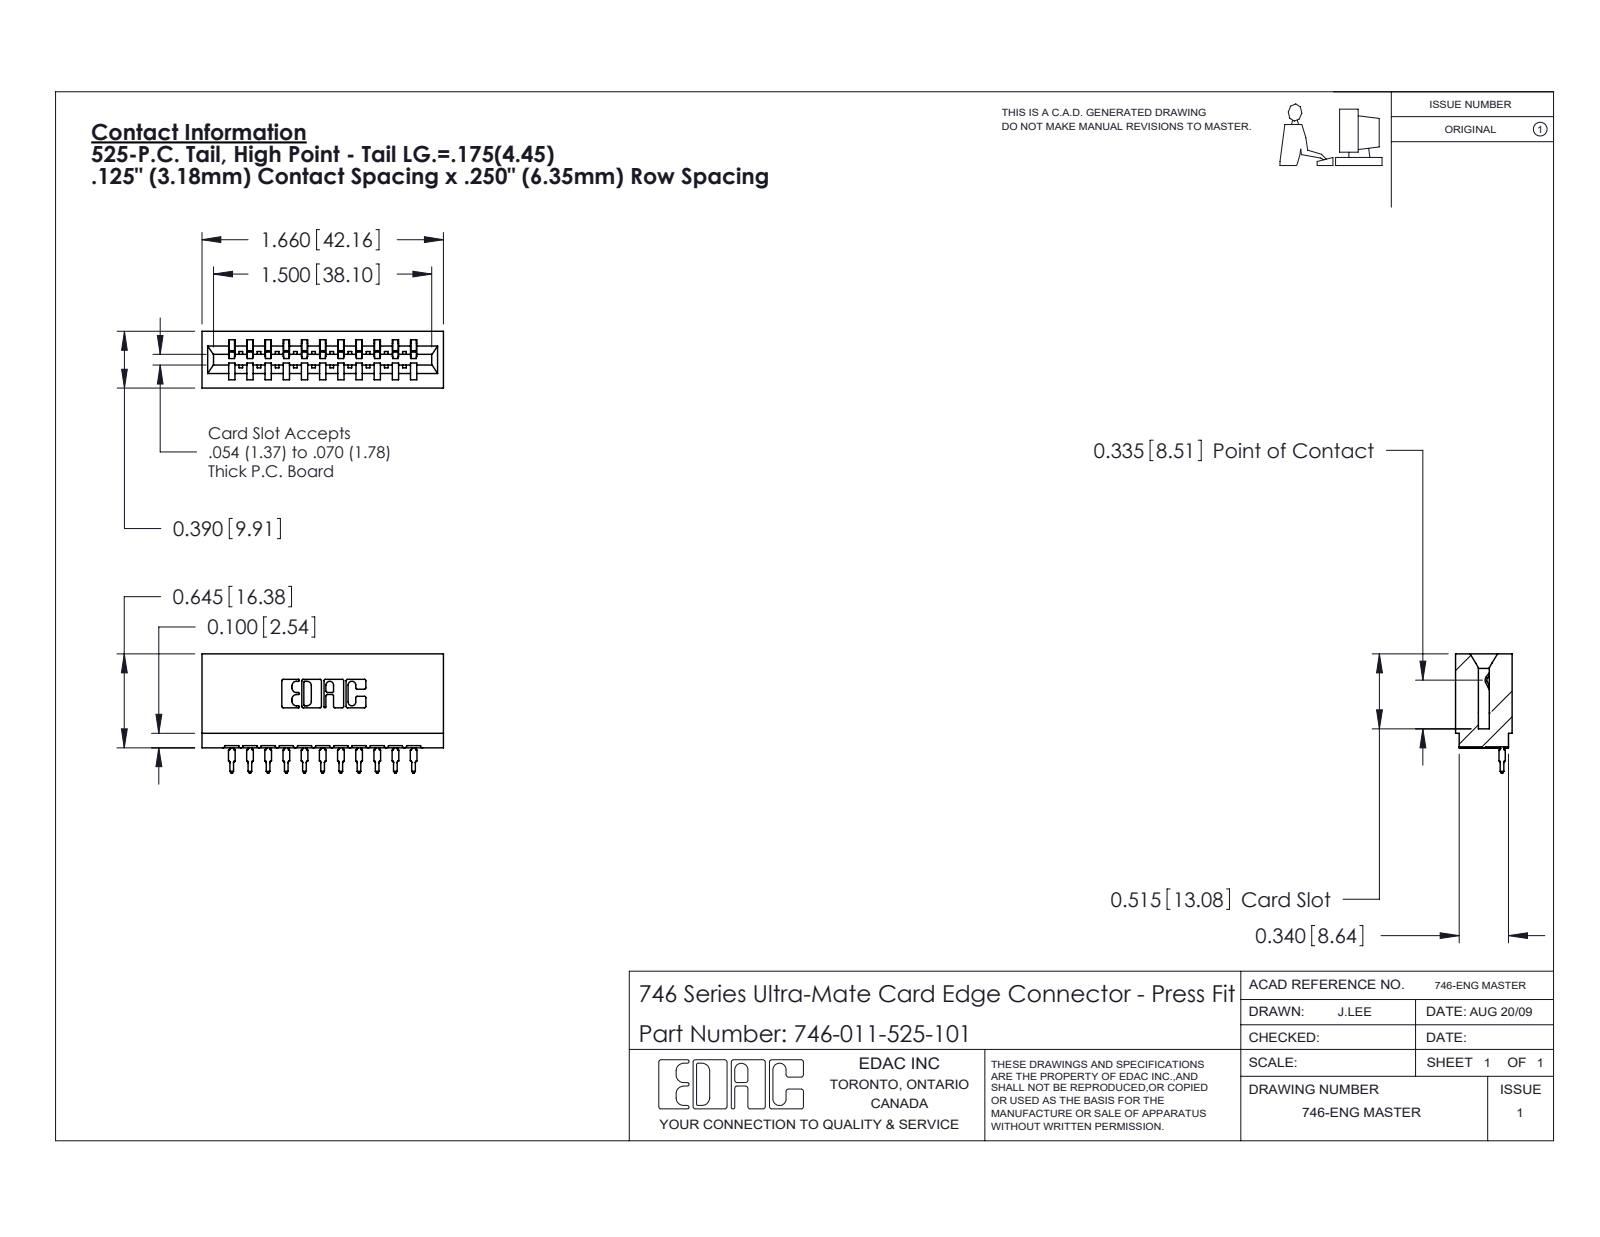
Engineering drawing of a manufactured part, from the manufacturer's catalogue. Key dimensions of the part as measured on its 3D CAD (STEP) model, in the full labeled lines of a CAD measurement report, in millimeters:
Part name (STEP PRODUCT): 746 Part_.515 Slot Depth - 01; 746-292-001_525; 746-011-525-101
STEP written by: SolidWorks 2020 (CONFIG_CONTROL_DESIGN)
Units: millimetres
Bodies: 12 solids, 1285 faces (748 planar, 251 cylindrical, 286 other)
Overall size (bounding box): 42.2 × 20.8 × 9.9
Volume: 4 600 mm³ · Surface area: 6 249 mm²
Partial cylindrical surfaces — rounded edges, fillets, slot ends (radius × count): R0.3 ×22, R0.5 ×22, R0.4 ×12, R0.2 ×6, R0.8 ×6, R0.1 ×4, R0.3 ×4, R0.7 ×3
Main face-to-face distances: 6.4, 8.5, 12.7, 1.4, 3.2, 3.2, 9.9, 1.1, 5.3, 7.4
